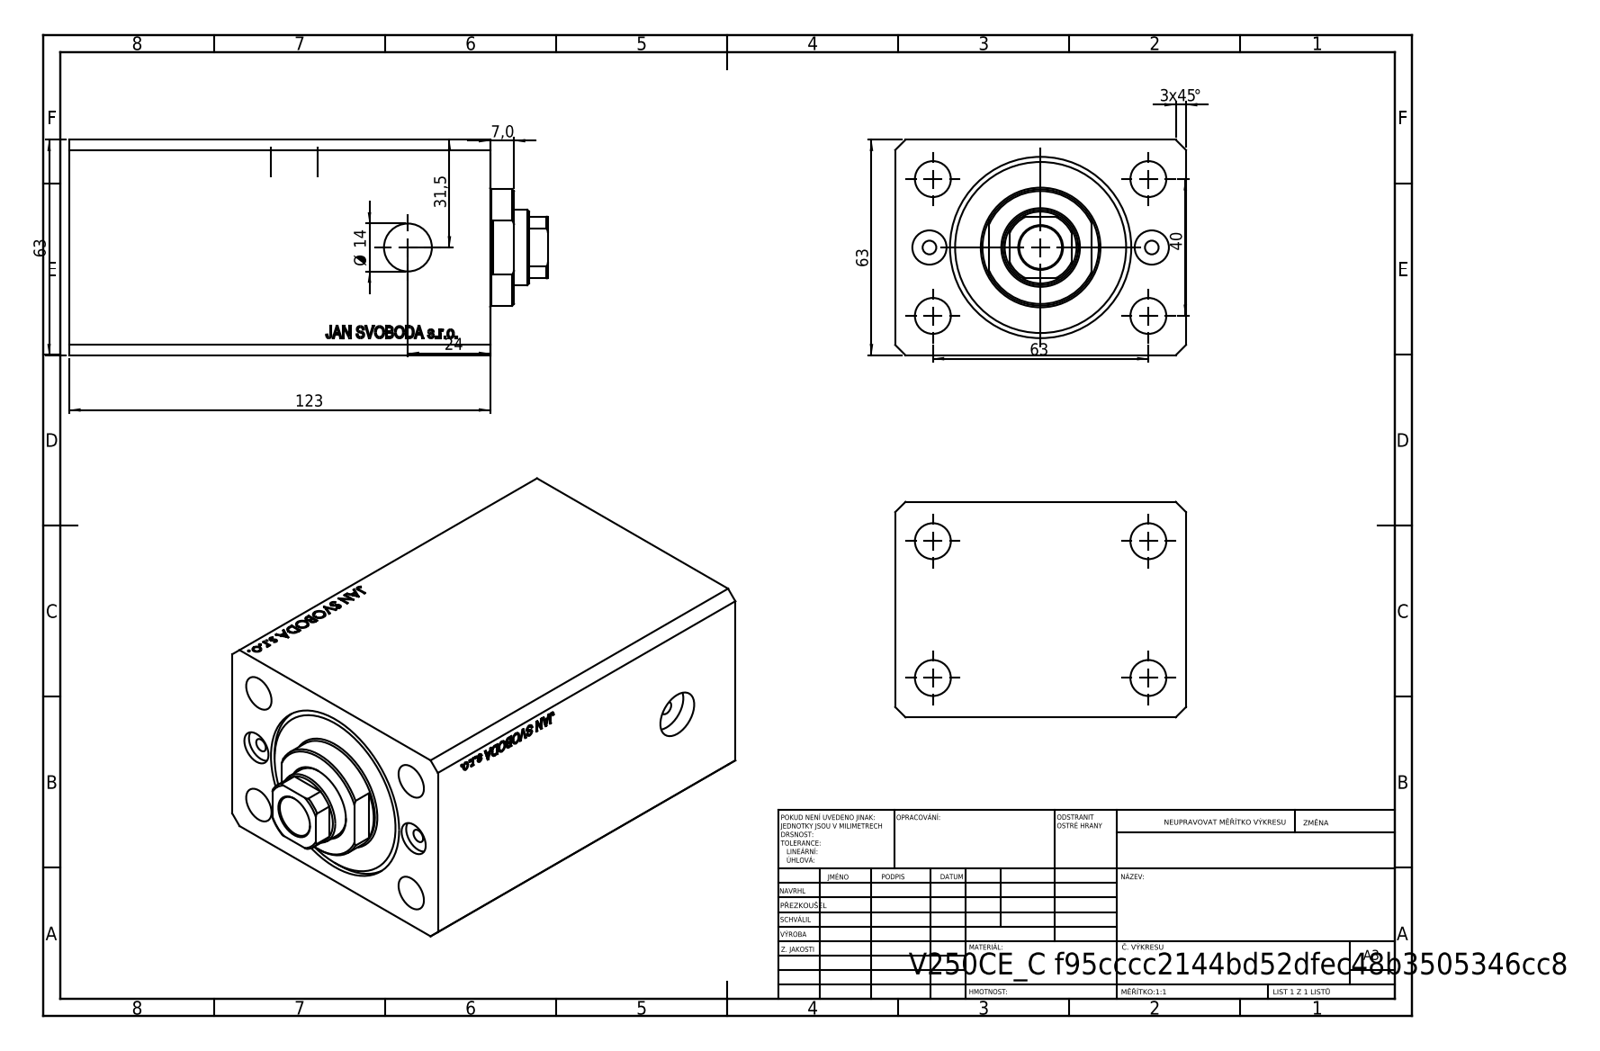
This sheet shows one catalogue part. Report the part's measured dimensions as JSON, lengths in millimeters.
{"part_name": "V250CE_C_VCP; V250CE_VC_C; V250CE_C_Body", "step_written_by": "SolidWorks 2019 (CONFIG_CONTROL_DESIGN)", "units": "millimeters", "bodies": {"solids": 3, "faces": 862, "planar": 428, "cylindrical": 42, "other": 392}, "overall_size": [139.9, 85, 63], "volume_mm3": 573545, "surface_area_mm2": 104259, "round_holes": [[10.5, 4], [4, 3], [10, 2], [14, 2], [12.5, 1], [22, 1], [40, 1], [53, 1]], "round_bosses_or_shafts": [[34, 1]], "partial_cylinders_radius": [[10.5, 1]], "face_to_face_distances": [63, 85, 123, 95.9, 27.1, 11.4, 84.5, 111.6, 100.4, 50], "hole_center_spacings": [20.02, 37.31, 67.05, 32.5, 40, 63, 74.63, 65]}
